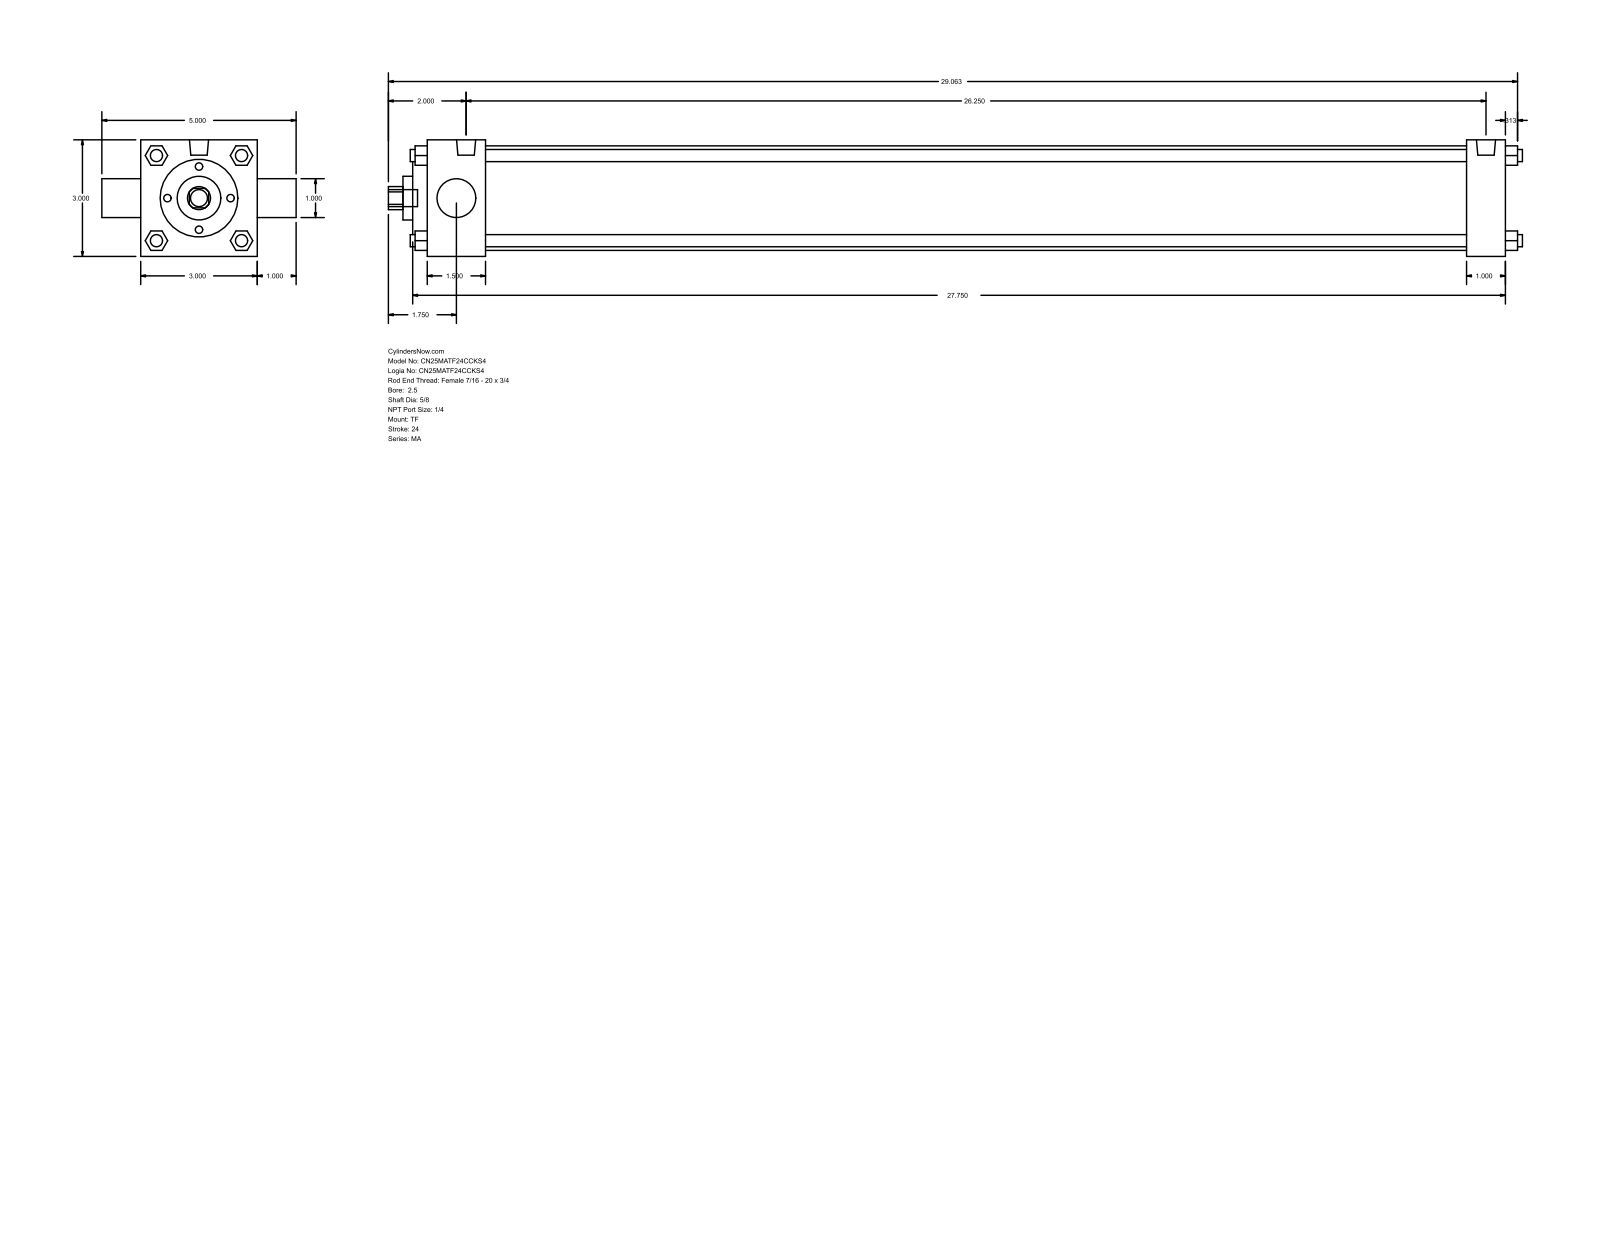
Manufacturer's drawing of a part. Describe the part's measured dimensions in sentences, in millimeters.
The part is named "MA_TF__0250_0.625". Its 3-D file was written by "GSSL Pune (CONFIG_CONTROL_DESIGN)". It is 0 solids with 122 faces: 93 planar, 29 cylindrical and 0 other. Overall it measures 741.36 by 127 by 76.2 millimeters. Round holes: 1 of diameter 15.88, 1 of diameter 25.4, 1 of diameter 28.57, 1 of diameter 50.8, 1 of diameter 68.33. Round bosses or shafts: 7 of diameter 7.94, 2 of diameter 12.49, 1 of diameter 11.11. Partial cylindrical surfaces (rounded edges, fillets, slot ends): 1 of radius 7.54. The main face-to-face distances are 76.2, 704.85, 25.4, 38.1, 679.45, 641.35, 666.75, 12.7, 9.52, 47.62.
